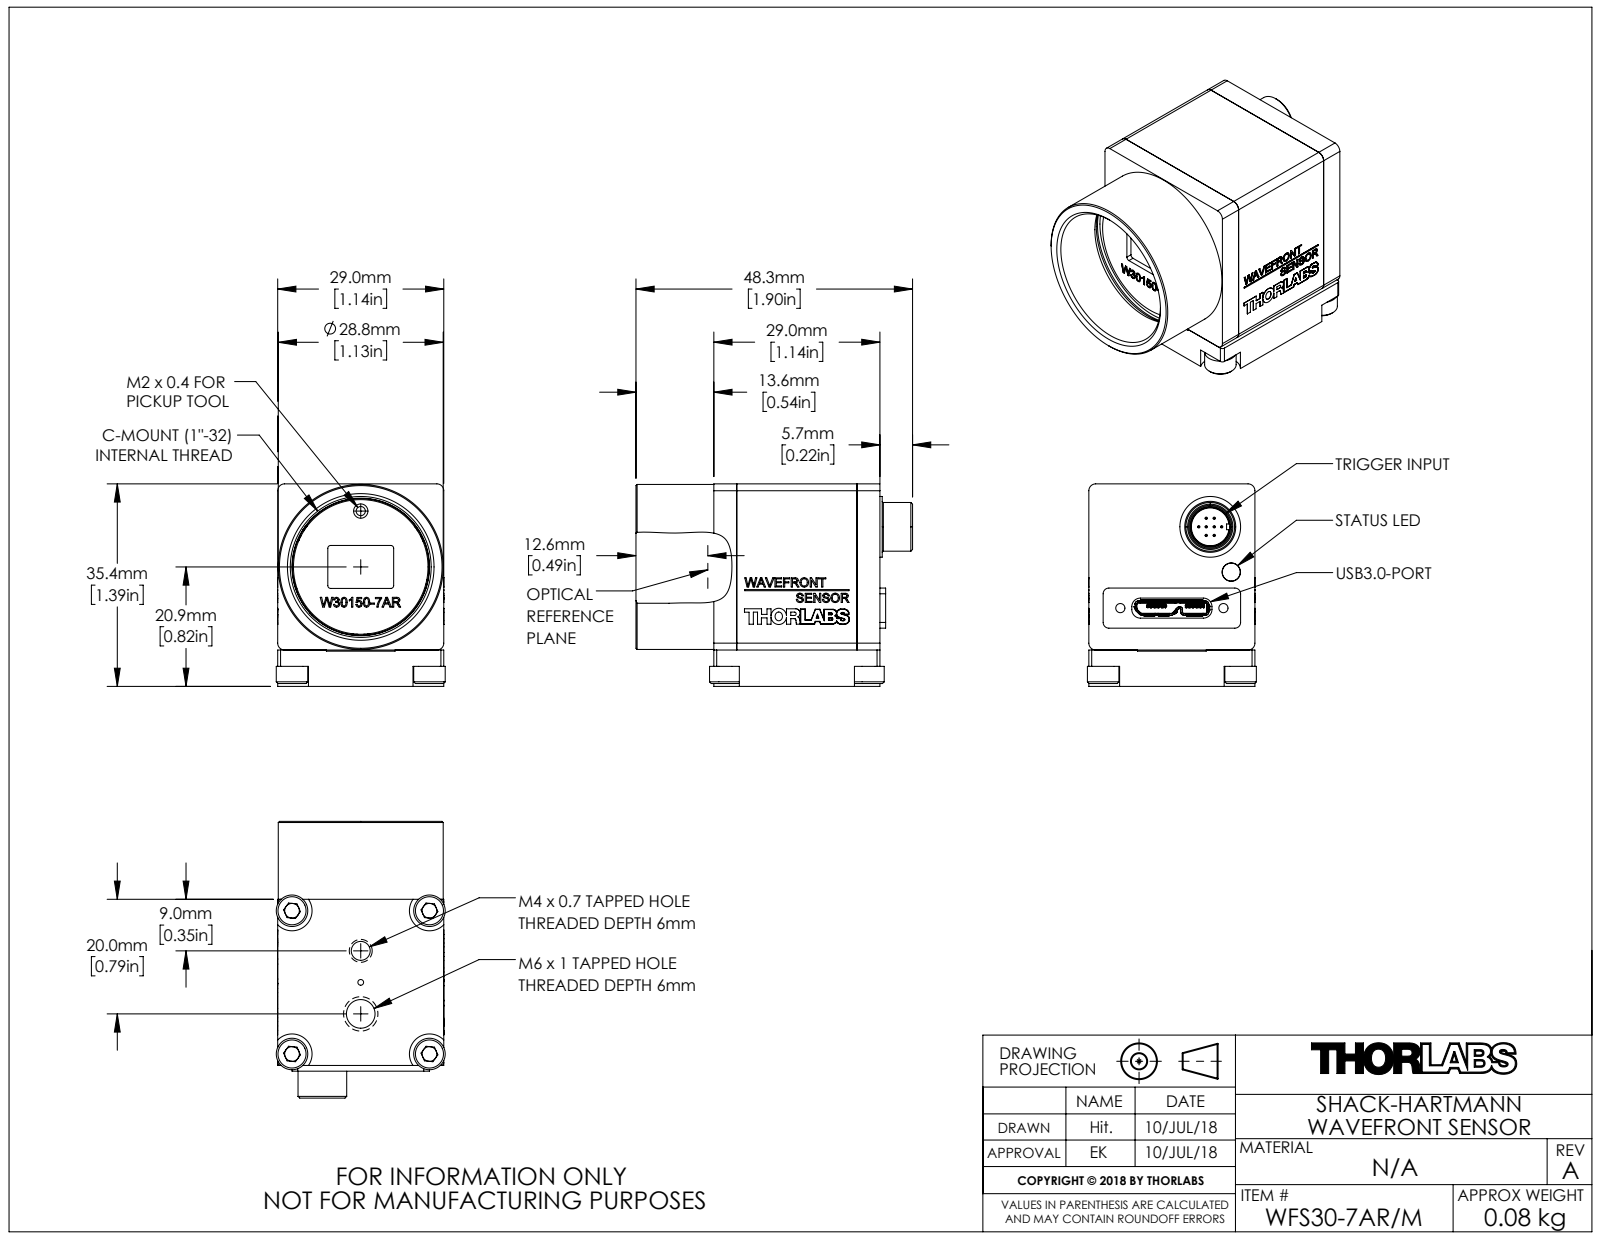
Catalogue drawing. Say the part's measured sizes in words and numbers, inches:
The part is named "MTN008521-E0W". Its 3-D file was written by "SolidWorks 2016 (AUTOMOTIVE_DESIGN)". It is 0 solids with 2614 faces: 1900 planar, 407 cylindrical and 307 other. Overall it measures 1.902 by 1.392 by 1.161 inches. Round holes: 11 of diameter 0.126, 5 of diameter 0.098, 3 of diameter 0.063, 3 of diameter 0.075, 1 of diameter 0.037, 1 of diameter 0.039, 1 of diameter 0.059, 1 of diameter 0.13, 1 of diameter 0.197, 1 of diameter 0.268, 1 of diameter 0.315, 1 of diameter 0.591. Round bosses or shafts: 8 of diameter 0.016, 6 of diameter 0.039, 5 of diameter 0.118, 4 of diameter 0.217, 1 of diameter 1.134, 1 of diameter 0.941, 1 of diameter 0.925, 1 of diameter 0.417. Partial cylindrical surfaces (rounded edges, fillets, slot ends): 37 of radius 0.02, 31 of radius 0.008, 29 of radius 0.006, 12 of radius 0.012, 11 of radius 0.039, 10 of radius 0.059, 8 of radius 0.004, 8 of radius 0.024. The main face-to-face distances are 1.142, 0.024, 1.118, 0.25, 0.039, 0.189, 1.392, 0.103, 1.094, 0.692. The hole center spacings are 0.384, 0.741, 0.383, 0.543, 0.665, 0.198, 0.547, 0.682.
